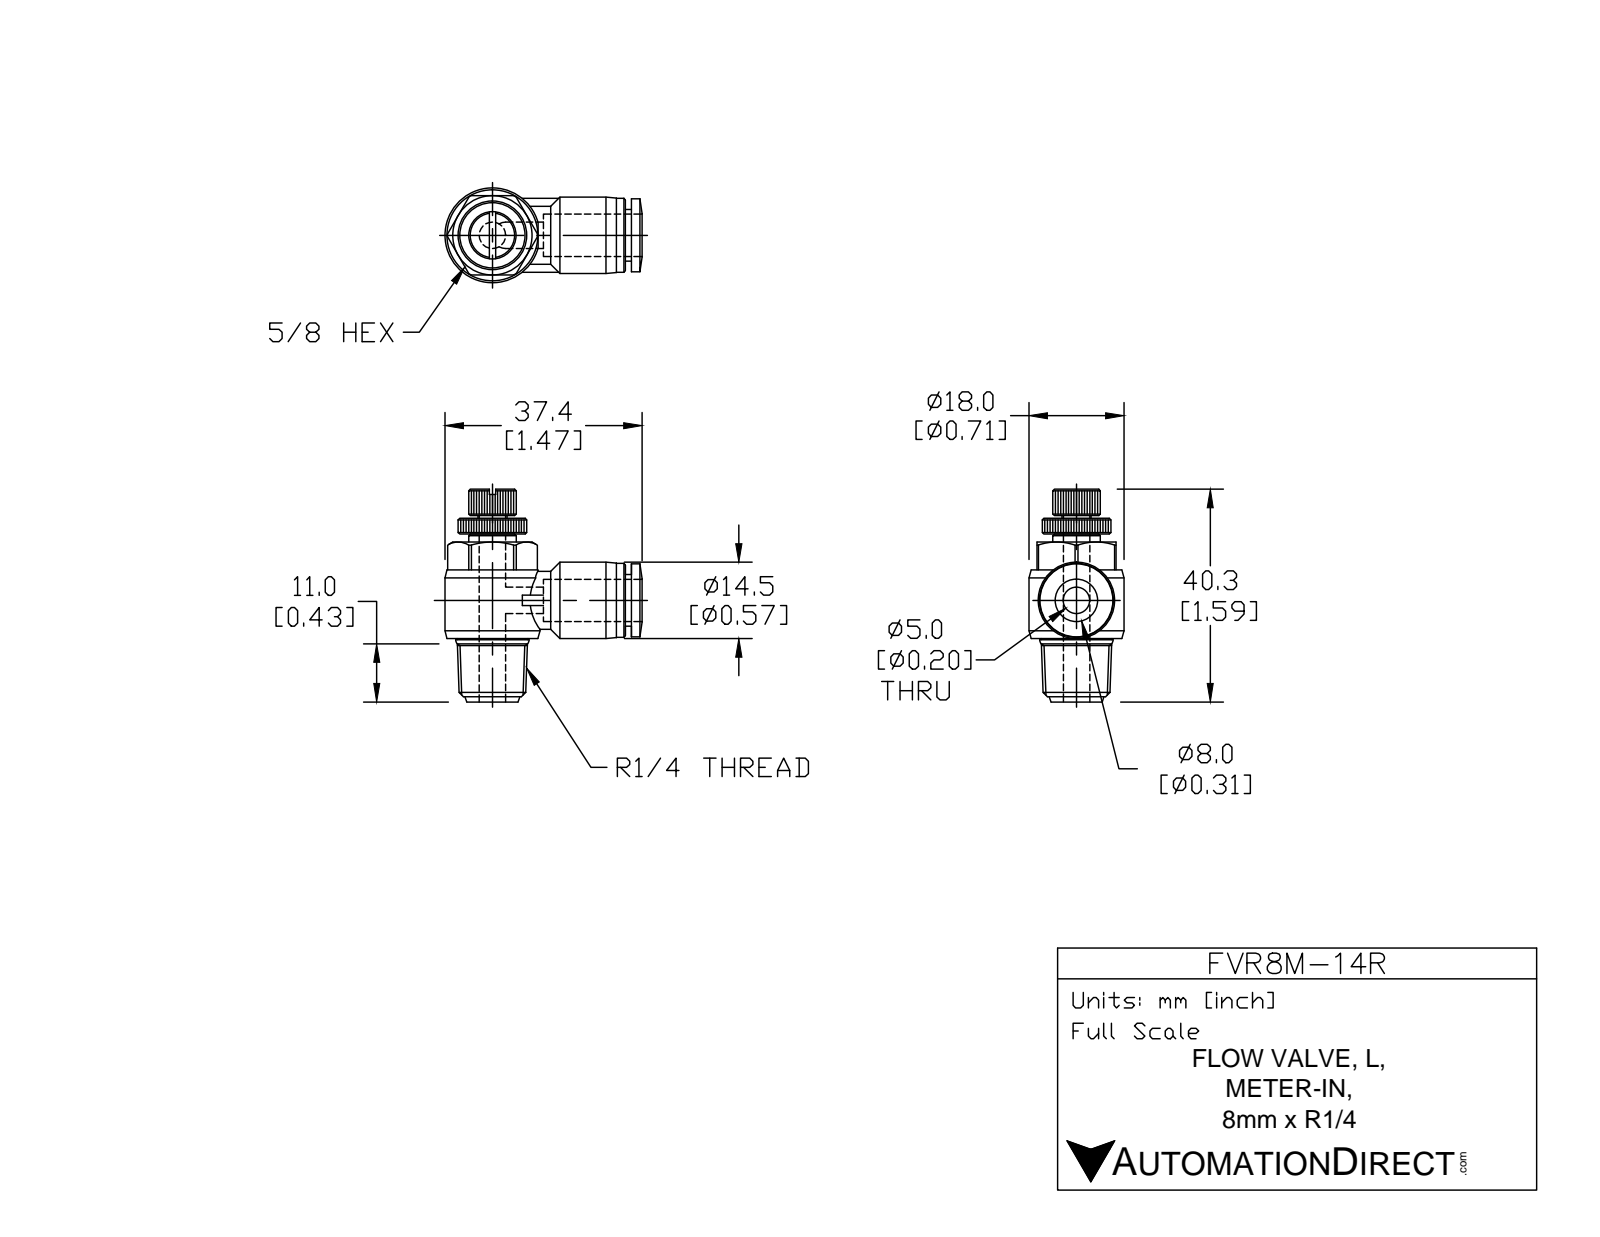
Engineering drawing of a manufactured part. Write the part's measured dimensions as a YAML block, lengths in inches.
part_name: "FVR8M-14R"
step_written_by: "SolidWorks 2015 (AUTOMOTIVE_DESIGN)"
units: inches
bodies: {solids: 1, faces: 418, planar: 187, cylindrical: 111, other: 120}
overall_size: [1.835, 1.47, 0.709]
volume: 0.495
surface_area: 7.06
round_holes:
  - {diameter: 0.177, count: 2}
  - {diameter: 0.327, count: 1}
round_bosses_or_shafts:
  - {diameter: 0.709, count: 1}
  - {diameter: 0.571, count: 1}
  - {diameter: 0.551, count: 1}
  - {diameter: 0.543, count: 1}
  - {diameter: 0.528, count: 1}
  - {diameter: 0.433, count: 1}
  - {diameter: 0.386, count: 1}
  - {diameter: 0.354, count: 1}
partial_cylinders:
  - {radius: 0.256, count: 1}
  - {radius: 0.335, count: 1}
face_to_face_distances: [0.591, 0.177, 0.701, 0.878, 1.173, 0.045, 0.76, 0.059, 0.118, 0.472]
